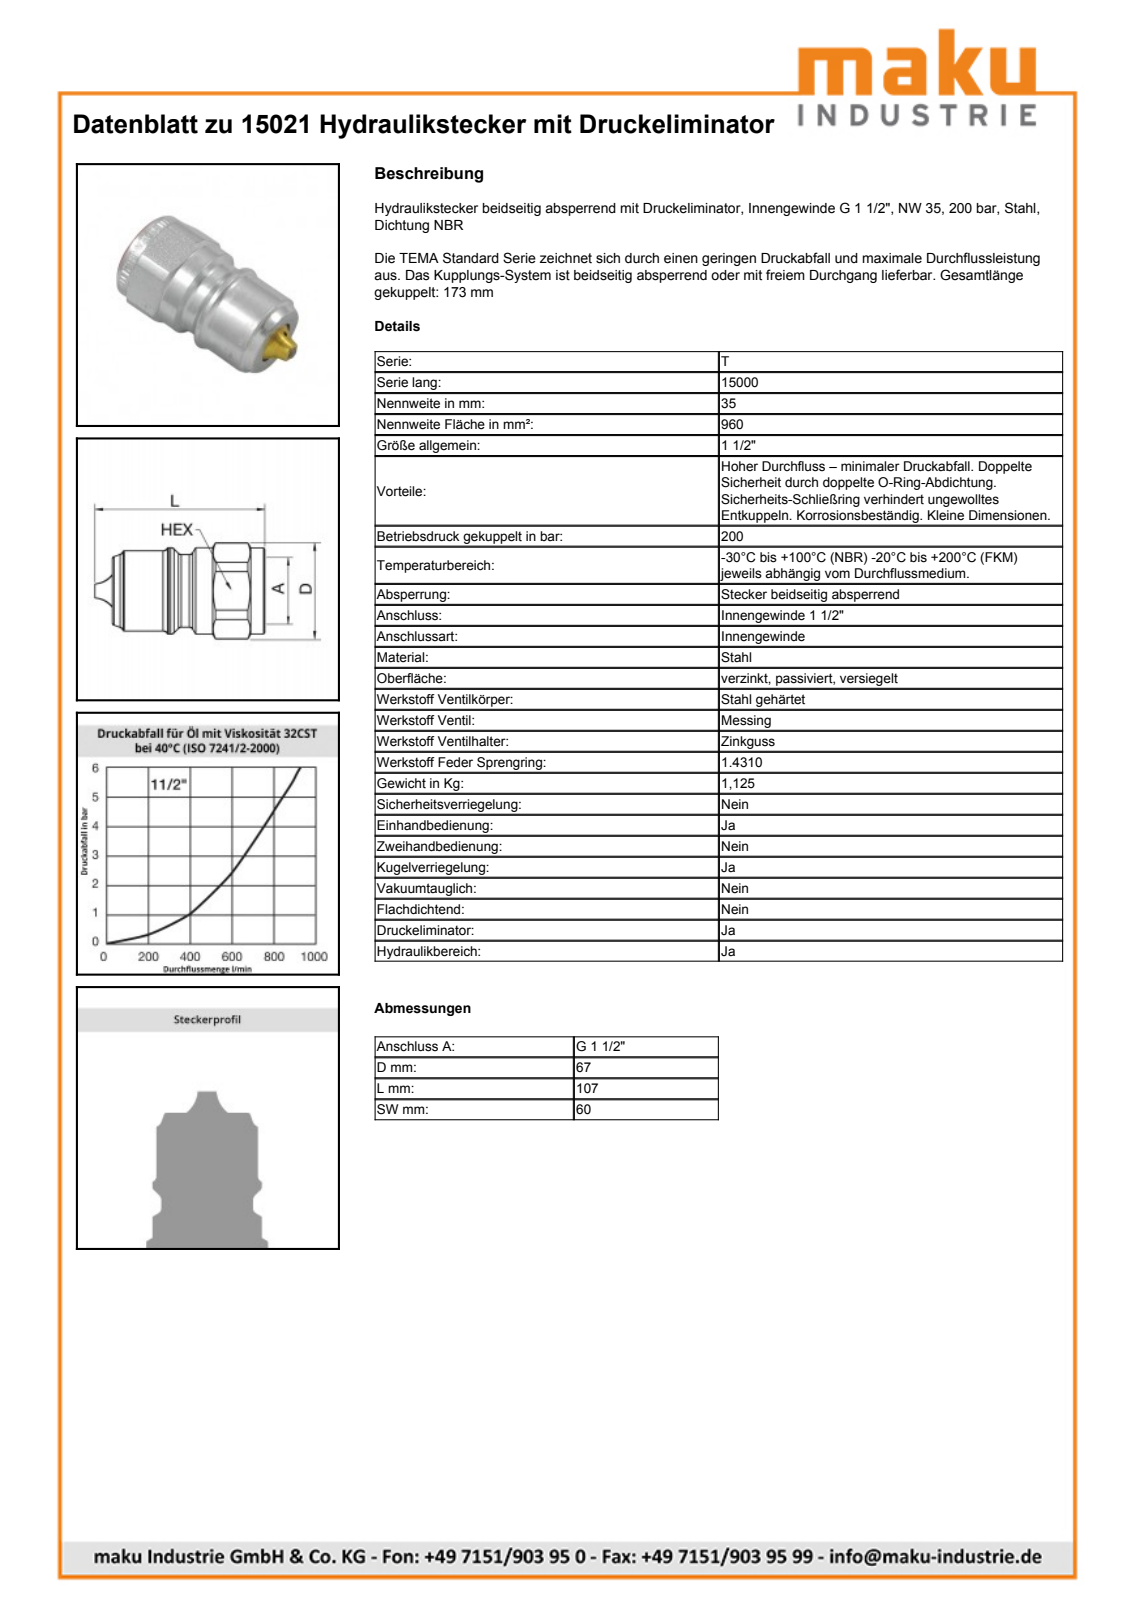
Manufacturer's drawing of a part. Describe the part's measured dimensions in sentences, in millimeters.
The part is named "15021". Its 3-D file was written by "SolidWorks 2009 (AUTOMOTIVE_DESIGN)". It is 1 solid with 94 faces: 22 planar, 28 cylindrical and 44 other. Overall it measures 107 by 67 by 67 millimeters. Its volume is 205 201 cubic millimeters and its surface area 35 578 square millimeters. Round holes: 1 of diameter 4.2, 1 of diameter 35.3, 1 of diameter 38.3, 1 of diameter 45. Round bosses or shafts: 1 of diameter 67, 1 of diameter 51.2, 1 of diameter 48.8, 1 of diameter 45.25, 1 of diameter 13.59, 1 of diameter 12.3, 1 of diameter 11.25, 1 of diameter 3.05. The main face-to-face distances are 60, 25.15, 34.85, 107, 81.85, 47, 61.48, 36.33, 1.48, 45.52.
